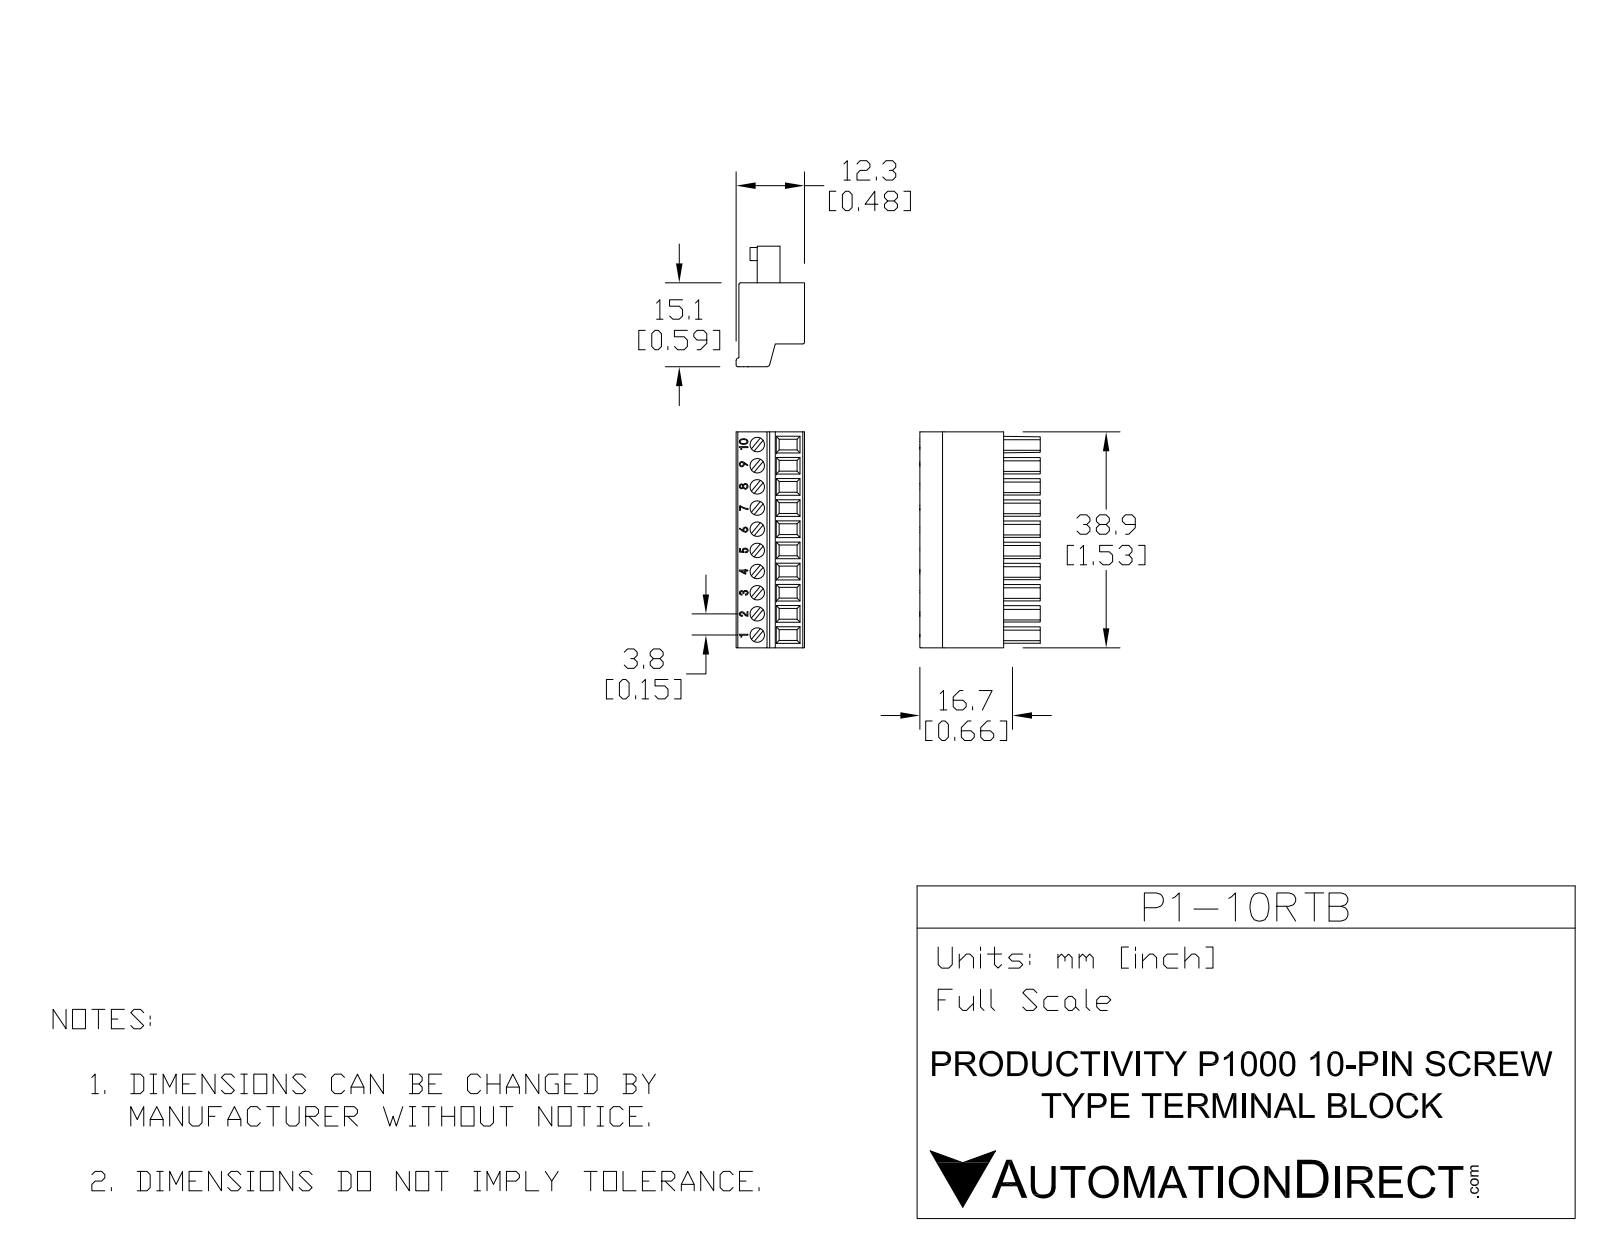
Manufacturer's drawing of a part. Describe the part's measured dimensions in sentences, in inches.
The part is named "P1-10 RTB". Its 3-D file was written by "SolidWorks 2016 (AUTOMOTIVE_DESIGN)". It is 1 solid with 456 faces: 303 planar, 75 cylindrical and 78 other. Overall it measures 1.531 by 0.855 by 0.484 inches. Its volume is 0.381 cubic inches and its surface area 6.694 square inches. Round holes: 10 of diameter 0.063, 10 of diameter 0.102. Partial cylindrical surfaces (rounded edges, fillets, slot ends): 20 of radius 0.008, 10 of radius 0.065, 3 of radius 0.012, 2 of radius 0.02. The main face-to-face distances are 0.15, 0.465, 0.3, 0.45, 0.6, 0.116, 0.034, 0.184, 0.75, 0.335. The hole center spacings are 0.15, 0.168, 0.3, 0.309, 0.45, 0.456, 0.6, 0.605.
